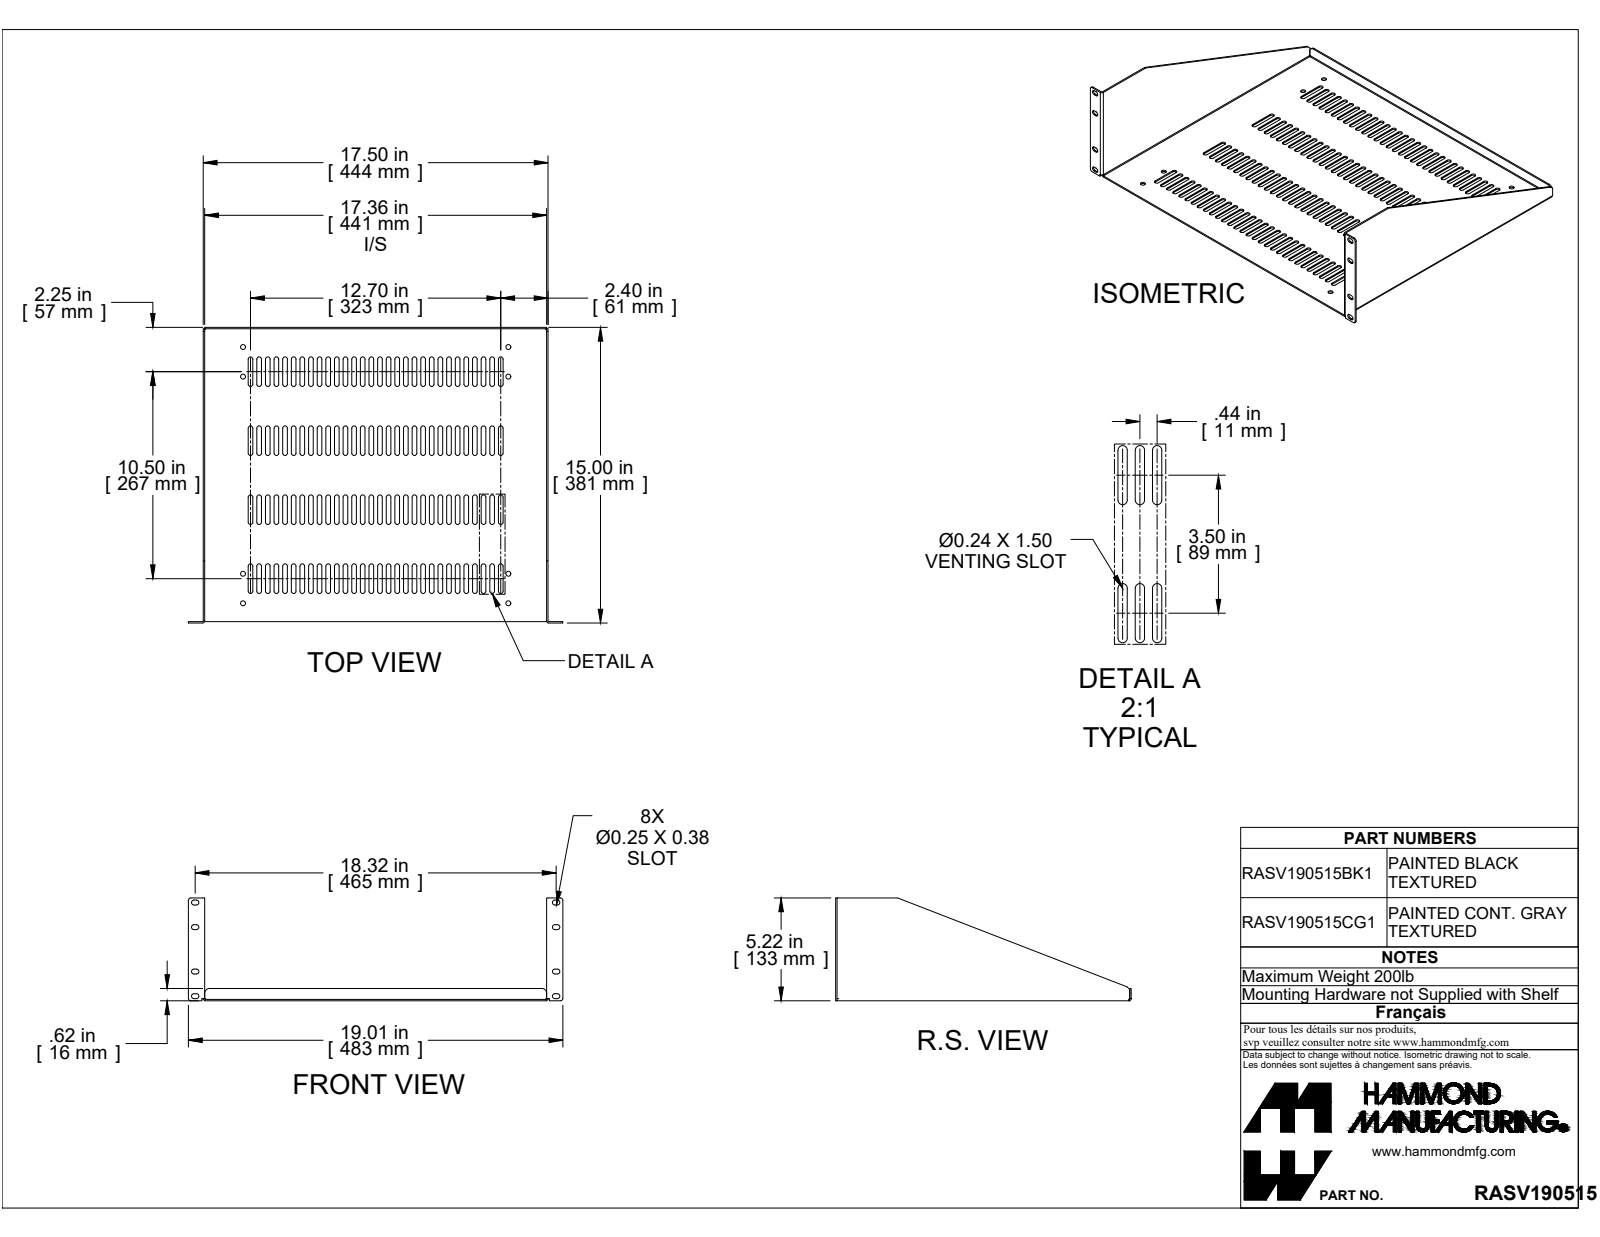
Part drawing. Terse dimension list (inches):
name: RASV190515BK1
written by: SolidWorks 2019 (CONFIG_CONTROL_DESIGN)
unit: in
bodies: 1 solid, 584 faces (296 planar, 284 cylindrical, 4 other)
size: 19.006 × 15 × 5.218
volume: 24.1 in³; area: 704.8 in²
holes: 8× ⌀0.25
rounds: 232× R0.118, 20× R0.125, 8× R0.117, 5× R0.036, 5× R0.108, 3× R0.055, 2× R0.25
face distances: 0.072, 17.428, 17.356, 17.5, 14.856, 14.928, 0.072, 14.928, 15, 0.876
hole spacings: 1.5, 11.5, 13.468, 13.551, 17.709, 10, 13, 16.774
